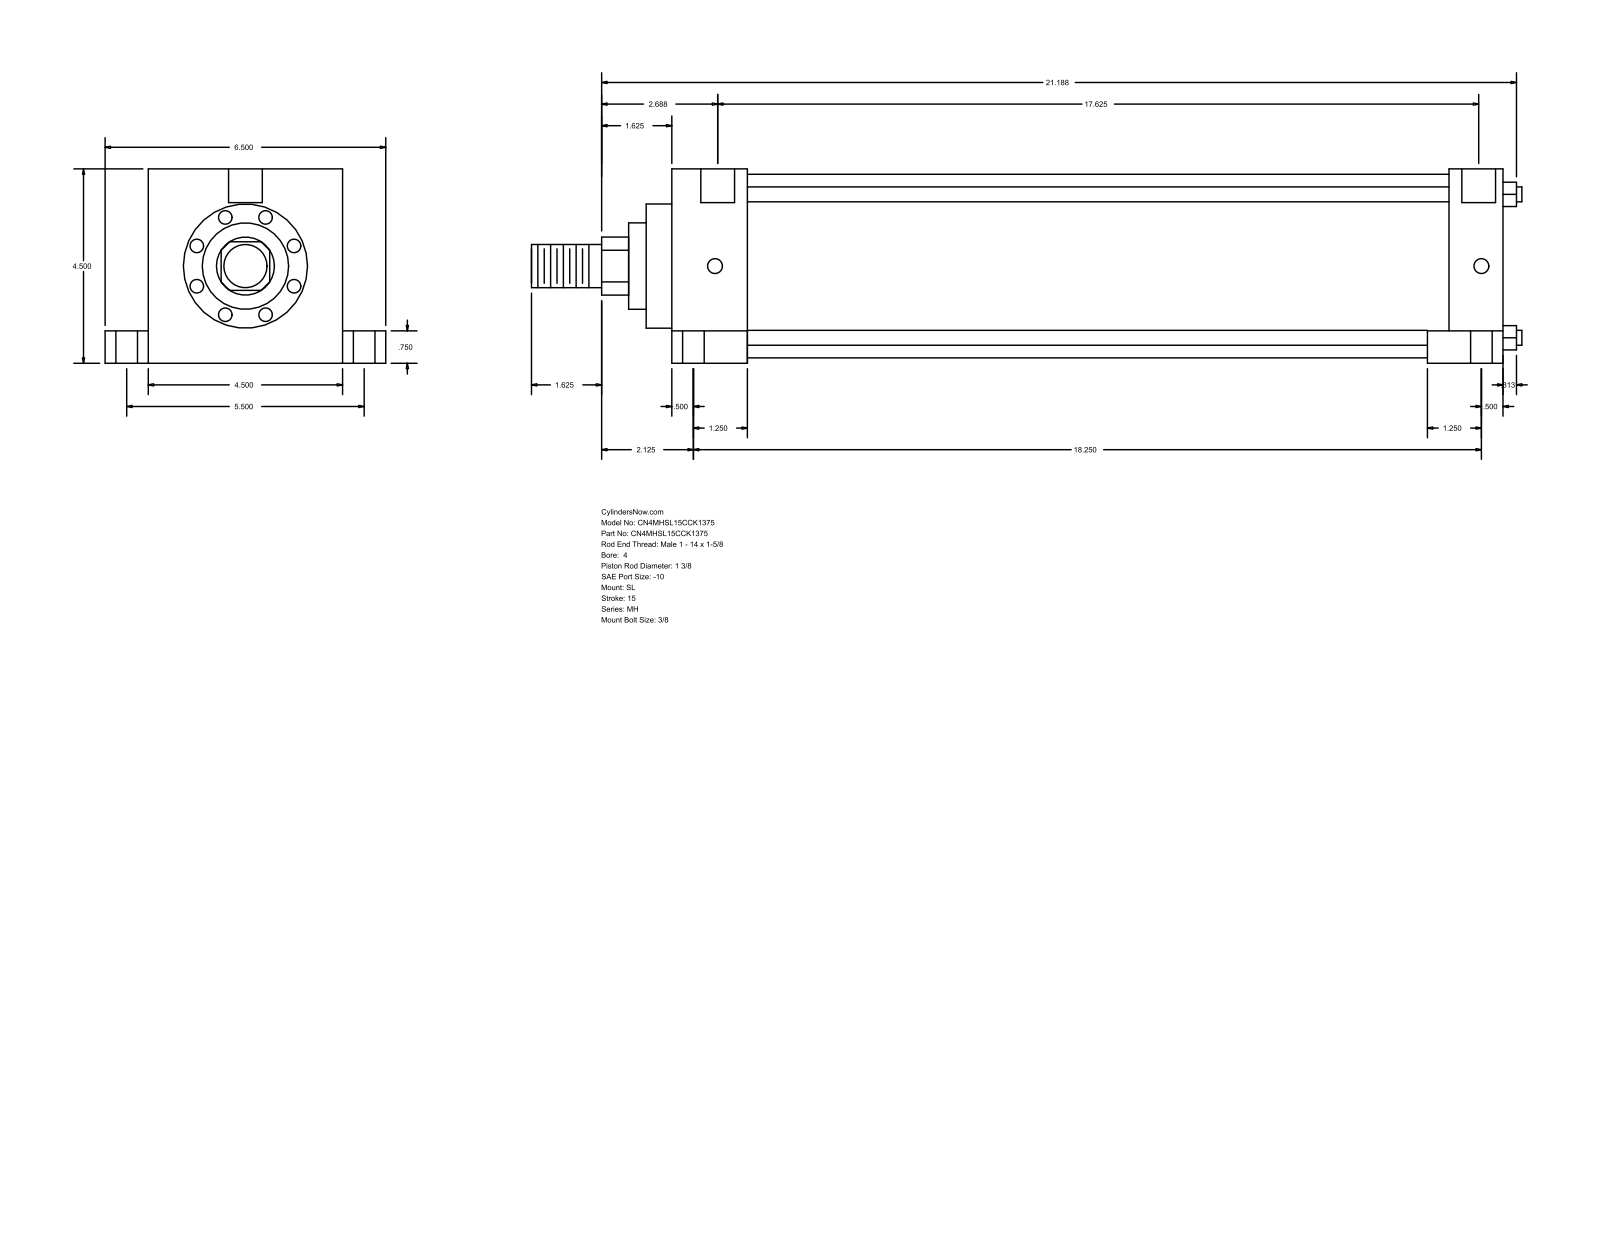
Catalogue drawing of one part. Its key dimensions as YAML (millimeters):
part_name: "MH_SL__0400_1.375"
step_written_by: "GSSL Pune (CONFIG_CONTROL_DESIGN)"
units: millimeters
bodies: {solids: 0, faces: 110, planar: 77, cylindrical: 33, other: 0}
overall_size: [582.61, 165.1, 114.3]
round_holes:
  - {diameter: 8.73, count: 4}
  - {diameter: 12.7, count: 4}
  - {diameter: 19.05, count: 4}
  - {diameter: 19.84, count: 2}
round_bosses_or_shafts:
  - {diameter: 8.76, count: 4}
  - {diameter: 107.95, count: 1}
  - {diameter: 73.03, count: 1}
  - {diameter: 50.8, count: 1}
  - {diameter: 34.92, count: 1}
  - {diameter: 25.4, count: 1}
partial_cylinders:
  - {radius: 17.06, count: 1}
face_to_face_distances: [114.3, 488.96, 44.45, 444.51, 457.21, 412.76, 31.75, 25.4, 139.7, 19.05]
hole_center_spacings: [69.85, 69.87, 70.99, 71.29, 139.7, 450.85, 454.66, 456.23]
